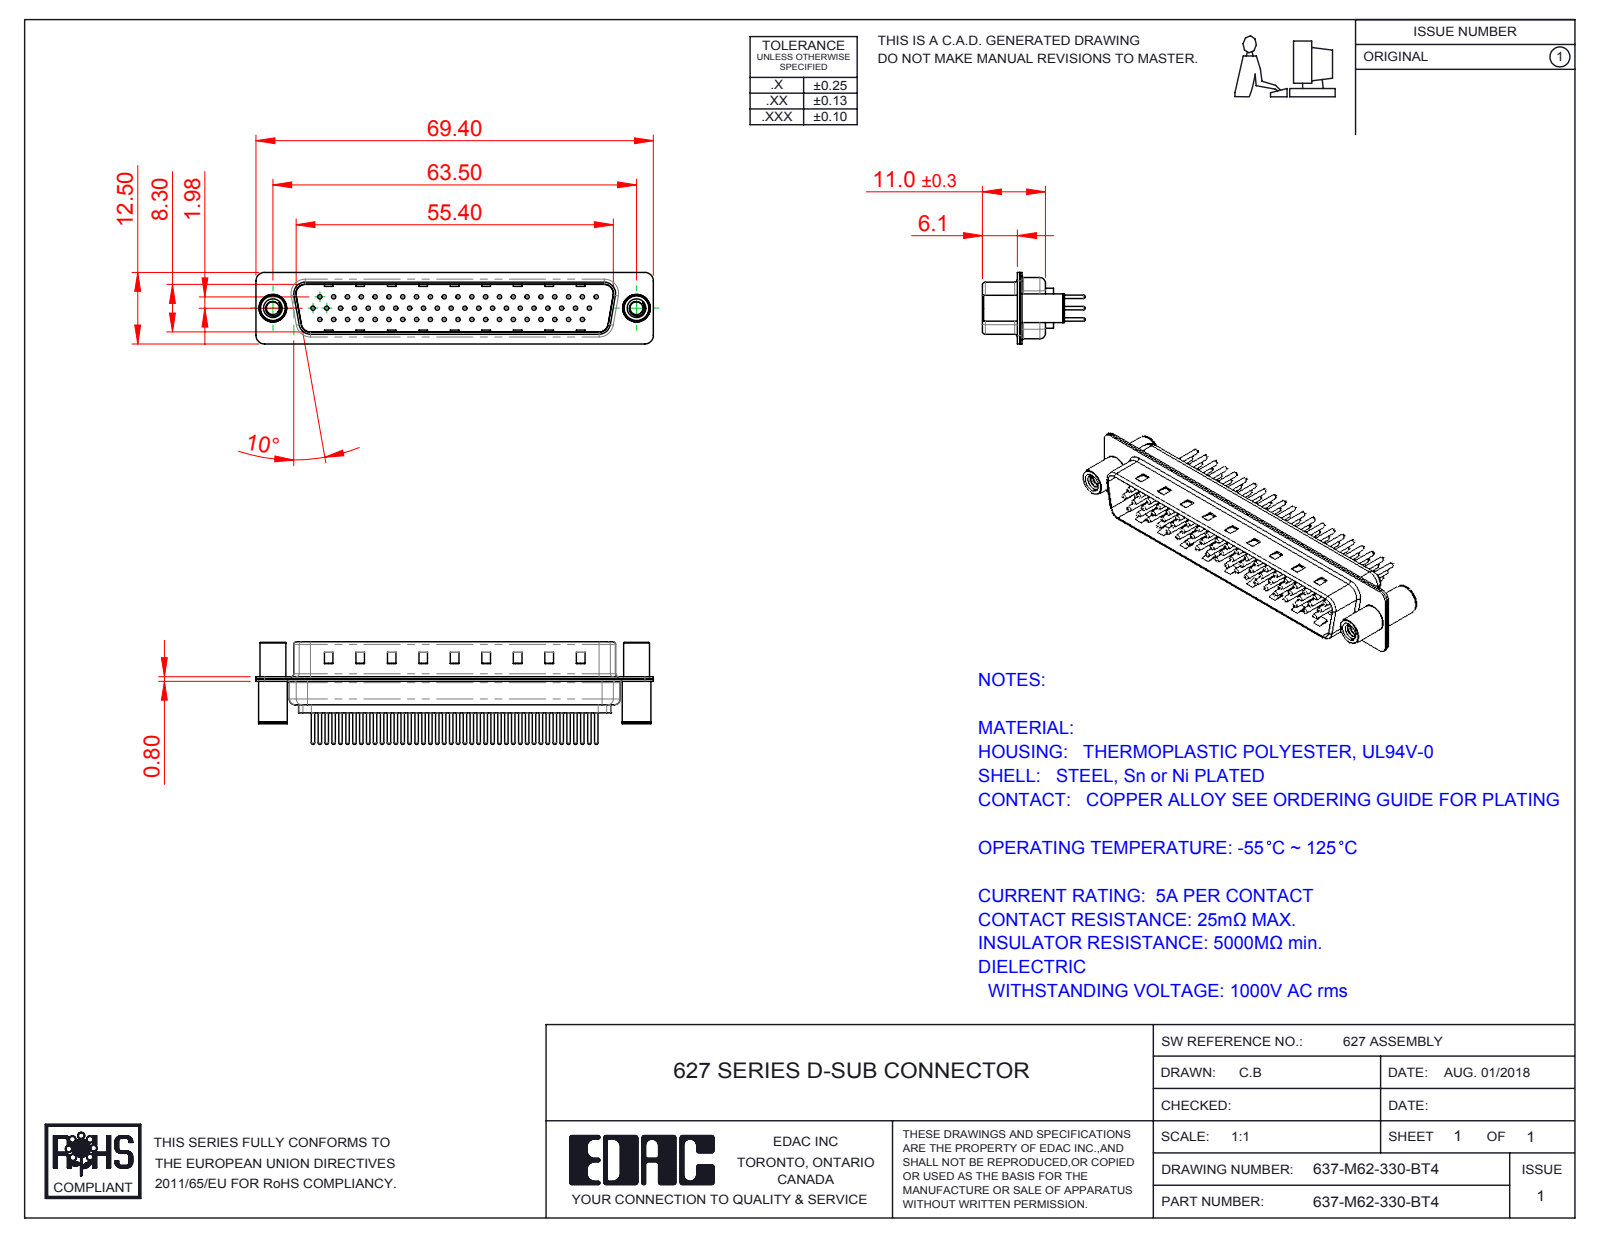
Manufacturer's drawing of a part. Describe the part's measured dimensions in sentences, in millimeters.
The part is named "637M Shell Front_62 Contacts; 637M Contact Row 2_30; 637M Contact Row 1_30; 637M Housing_62 Contacts (+4 more)". Its 3-D file was written by "SolidWorks 2016 (CONFIG_CONTROL_DESIGN)". It is 67 solids with 2792 faces: 643 planar, 1061 cylindrical and 1088 other. Overall it measures 69.4 by 17.9 by 12.5 millimeters. Its volume is 4 205 cubic millimeters and its surface area 11 942 square millimeters. Round holes: 62 of diameter 0.75, 62 of diameter 1.6, 62 of diameter 2, 2 of diameter 2.26, 2 of diameter 3.26, 2 of diameter 4, 2 of diameter 4.8. Round bosses or shafts: 62 of diameter 1.5, 62 of diameter 0.6, 2 of diameter 5, 2 of diameter 4.9, 2 of diameter 4.5. Partial cylindrical surfaces (rounded edges, fillets, slot ends): 16 of radius 1.5, 12 of radius 2, 8 of radius 0.5, 8 of radius 1.6, 4 of radius 0.25, 4 of radius 0.6, 4 of radius 0.65, 4 of radius 0.9. The main face-to-face distances are 0.4, 0.8, 9.5, 9.1, 8.7, 9.9, 0.75, 0.35, 5.9, 1.2. The hole center spacings are 7.24, 2.32, 2.41, 4.13, 9.65, 4.83, 14.48, 11.04.
